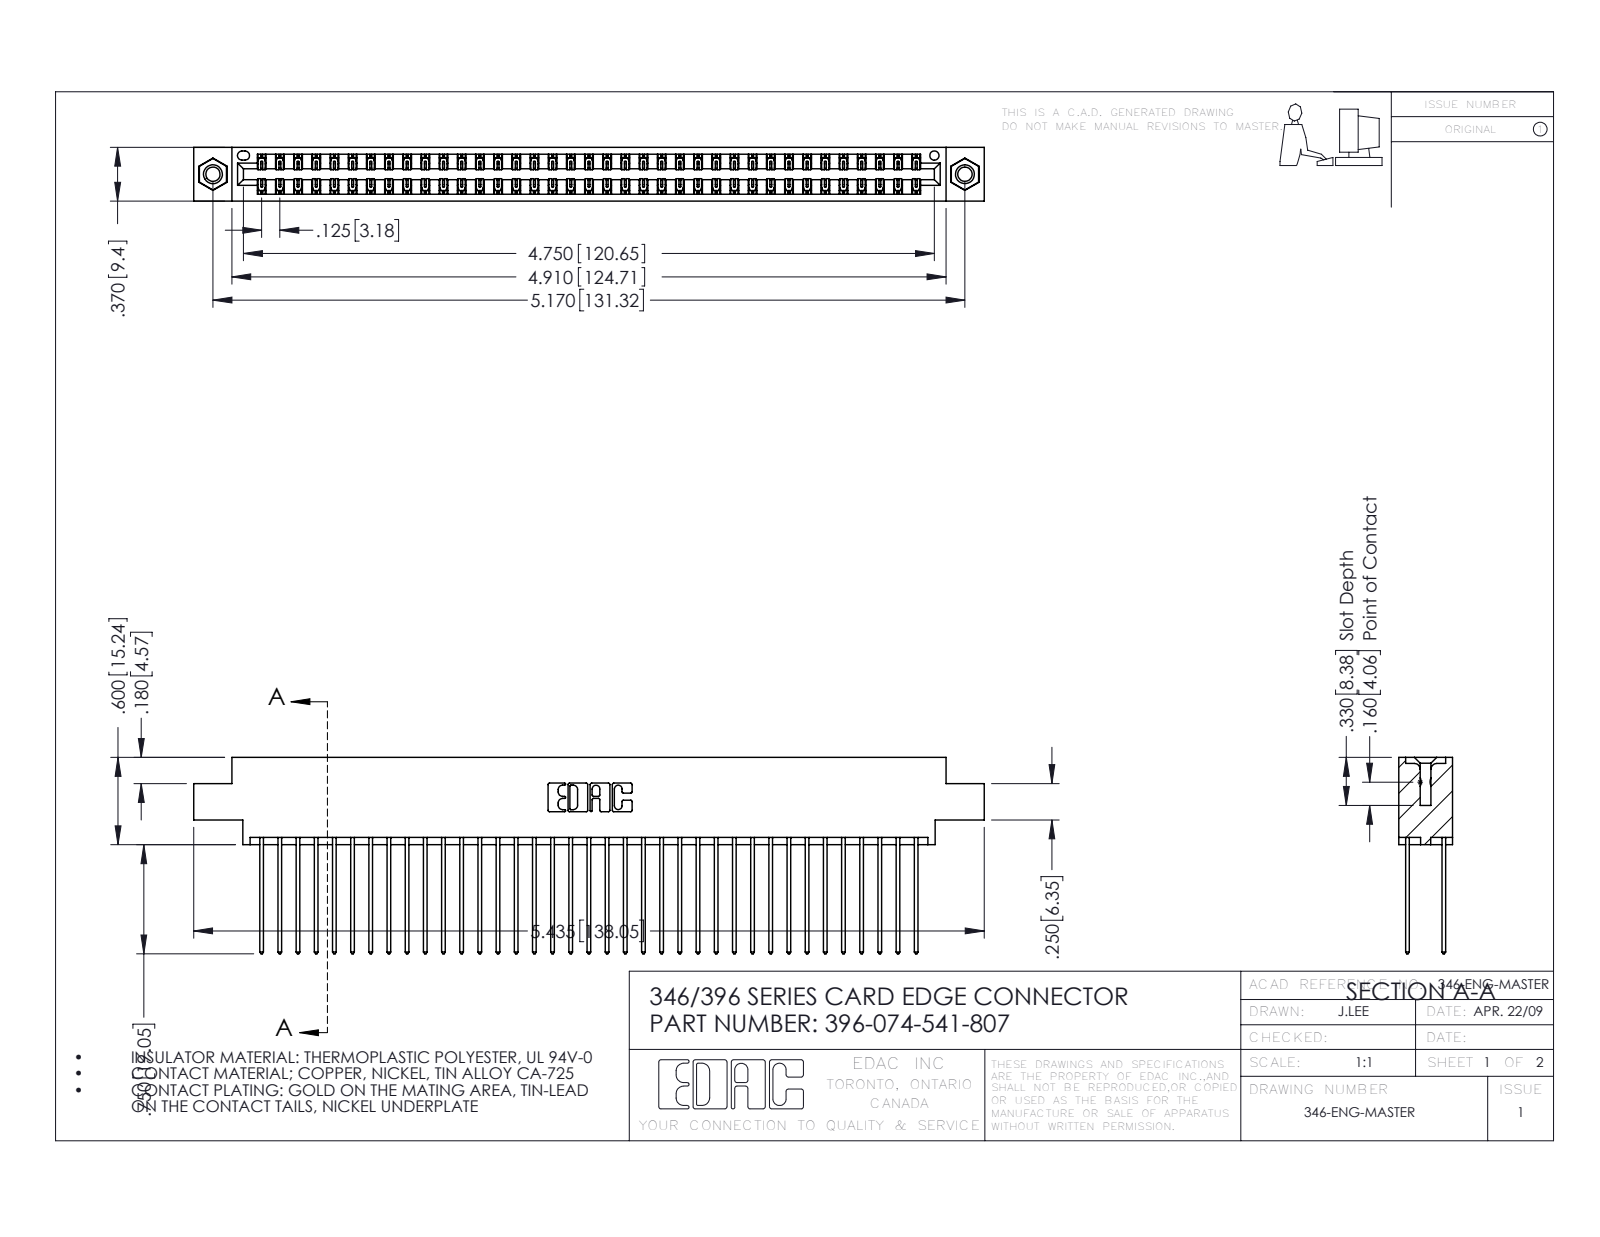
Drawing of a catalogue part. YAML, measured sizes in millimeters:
part_name: "396-074-541-807; 346 Part_0.170 Offset - 0.156 Dia-TI; 345-250-001_345-250-005-103; 345-292-001_345-293-141"
step_written_by: "SolidWorks 2016 (CONFIG_CONTROL_DESIGN)"
units: millimeters
bodies: {solids: 77, faces: 4034, planar: 2702, cylindrical: 1316, other: 16}
overall_size: [138, 34.3, 9.4]
volume: 13700
surface_area: 20970
round_holes:
  - {diameter: 2.5, count: 2}
  - {diameter: 3.2, count: 2}
  - {diameter: 4, count: 2}
  - {diameter: 1.6, count: 1}
round_bosses_or_shafts:
  - {diameter: 3.9, count: 2}
partial_cylinders:
  - {radius: 0.2, count: 111}
  - {radius: 0.3, count: 74}
  - {radius: 0.3, count: 22}
  - {radius: 0.2, count: 6}
  - {radius: 0.8, count: 6}
  - {radius: 0.7, count: 3}
  - {radius: 0.4, count: 2}
  - {radius: 0.6, count: 2}
face_to_face_distances: [1.2, 8.2, 6.4, 1.8, 7.6, 0.6, 9.4, 7, 5.6, 5.7]
hole_center_spacings: [6.2, 126, 131.3]
